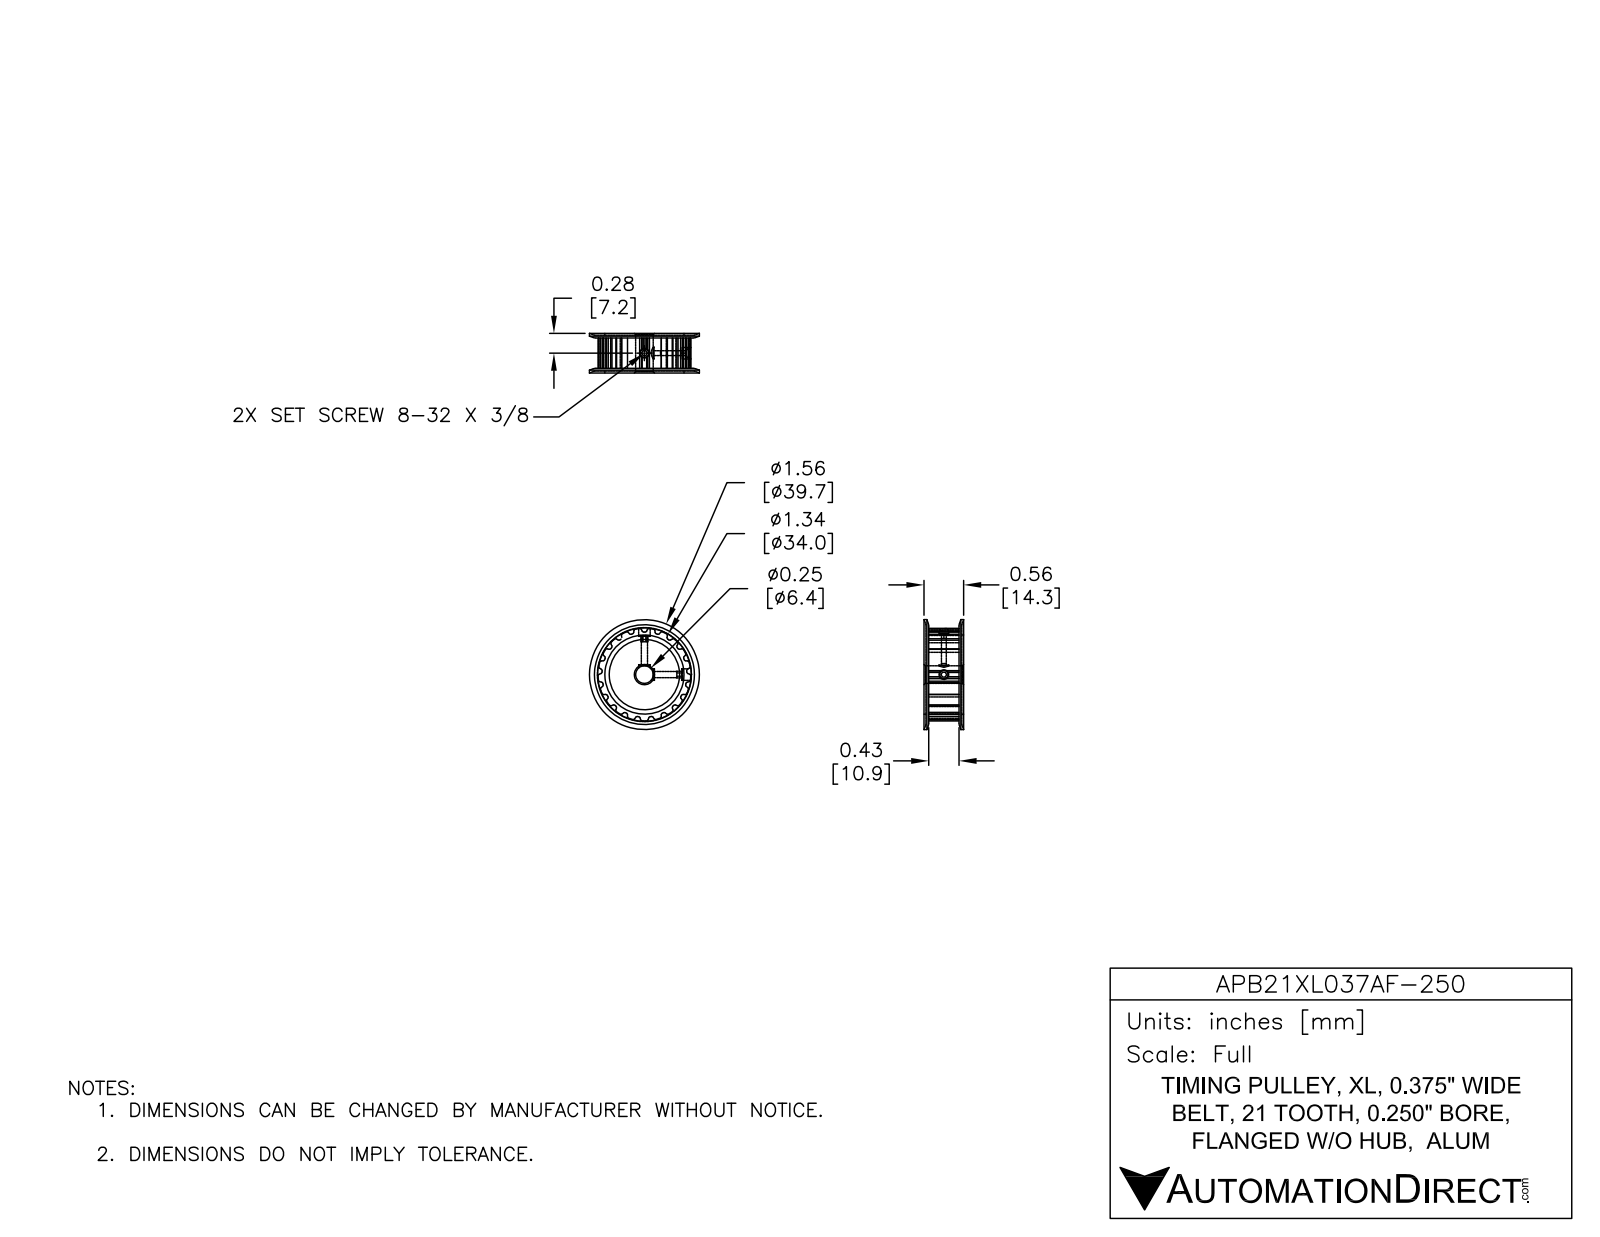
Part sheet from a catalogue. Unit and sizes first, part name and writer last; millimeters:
Units: millimetres
Overall size (bounding box): 39.7 × 39.7 × 14.3
Round holes (diameter × count): ⌀2.2 ×2, ⌀3.2 ×1, ⌀6.4 ×1
Round bosses / shafts (diameter × count): ⌀12.6 ×1
Partial cylindrical surfaces — rounded edges, fillets, slot ends (radius × count): R0.4 ×84, R1.6 ×1, R15.3 ×1
Main face-to-face distances: 12.7, 0.8, 13.5, 1.6, 11.9, 14.3, 11.1
Volume: 10 700 mm³ · Surface area: 5 450 mm²
Bodies: 1 solid, 233 faces (72 planar, 141 cylindrical, 20 other)
Part name (STEP PRODUCT): APB21XL037AF-250
STEP written by: SolidWorks 2014 (AUTOMOTIVE_DESIGN)
